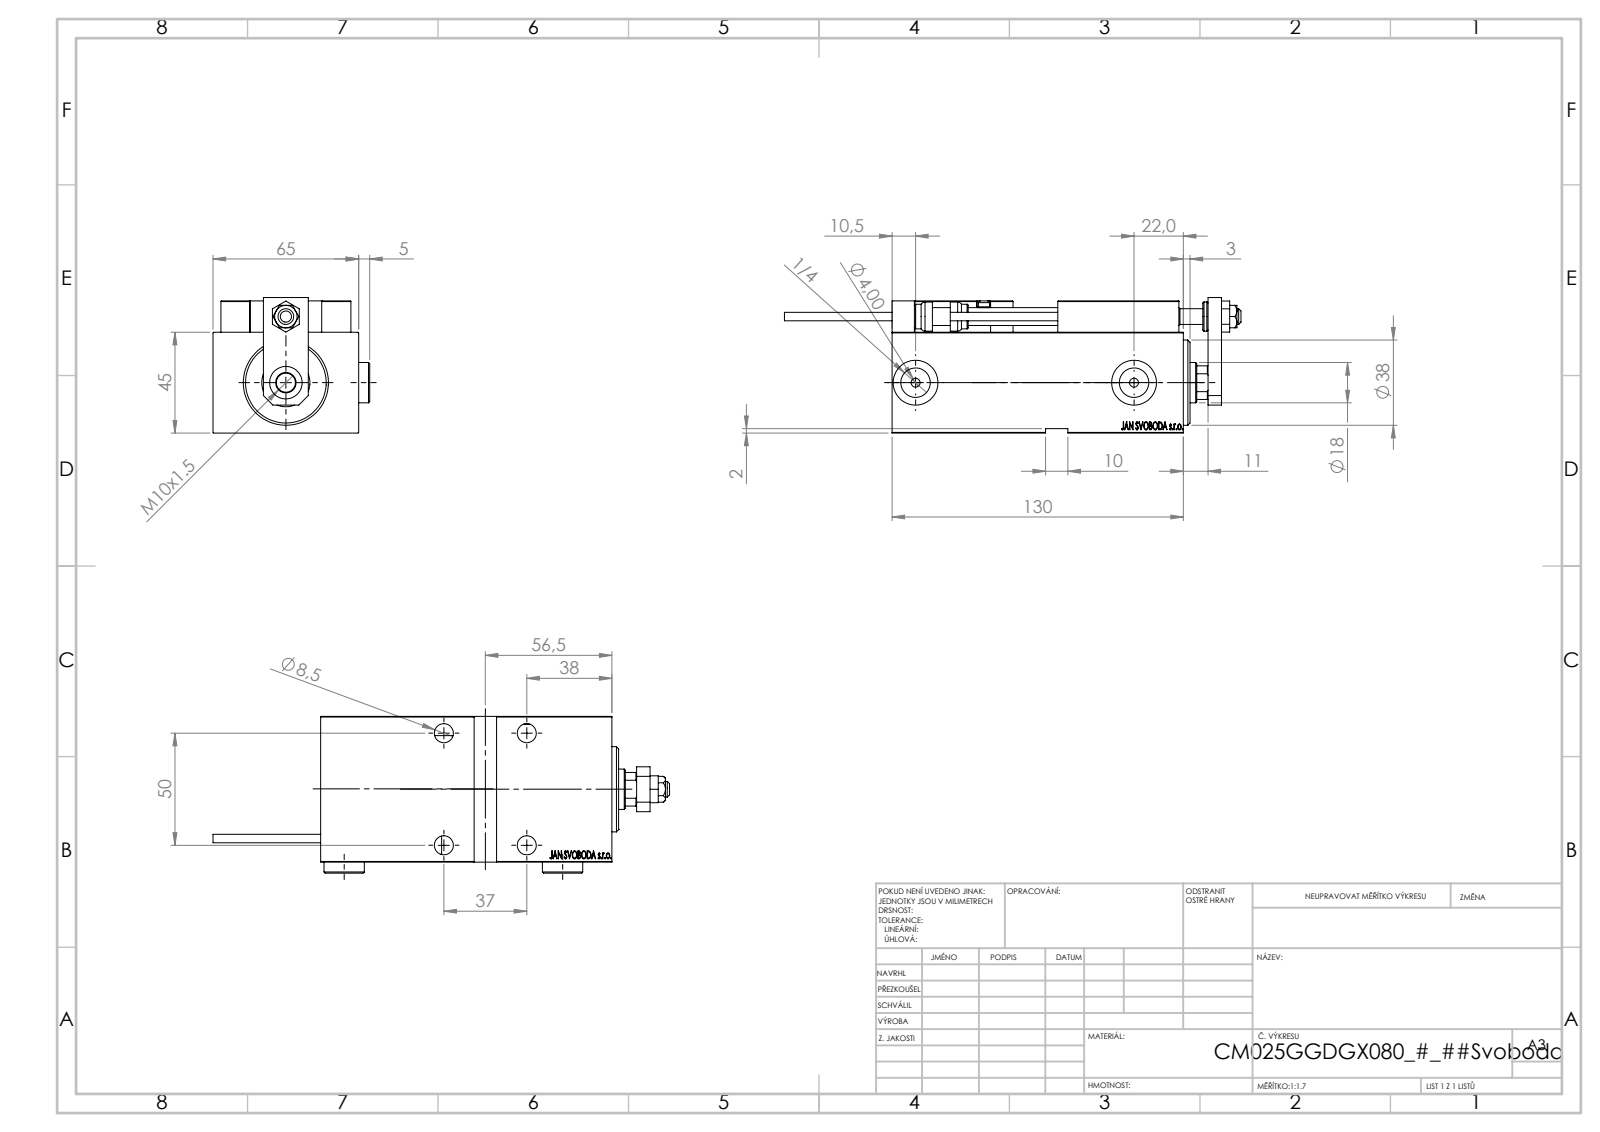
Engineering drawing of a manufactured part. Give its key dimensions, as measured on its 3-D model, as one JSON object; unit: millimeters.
{"part_name": "KONCOVKA; NUT_D12; ALLEN BOLT D5; V450CM_G_VCP (+7 more)", "step_written_by": "SolidWorks 2019 (CONFIG_CONTROL_DESIGN)", "units": "millimeters", "bodies": {"solids": 26, "faces": 1350, "planar": 605, "cylindrical": 200, "other": 545}, "overall_size": [203.7, 69.9, 60.5], "volume_mm3": 392699, "surface_area_mm2": 92220, "round_holes": [[4, 6], [8, 5], [8.5, 5], [3.2, 4], [13.5, 4], [5, 2], [13.16, 2], [20, 2], [7, 1], [14.5, 1], [18, 1], [21.5, 1]], "round_bosses_or_shafts": [[18, 2], [5, 2], [3.8, 2], [38, 1], [13, 1], [11, 1]], "partial_cylinders_radius": [[0.3, 30], [3, 2], [8.5, 1]], "face_to_face_distances": [45, 65, 14, 6, 59, 13, 130, 3.5, 141, 5], "hole_center_spacings": [11.37, 20, 29.59, 29.69, 34.44, 36.06, 37, 42.19]}
